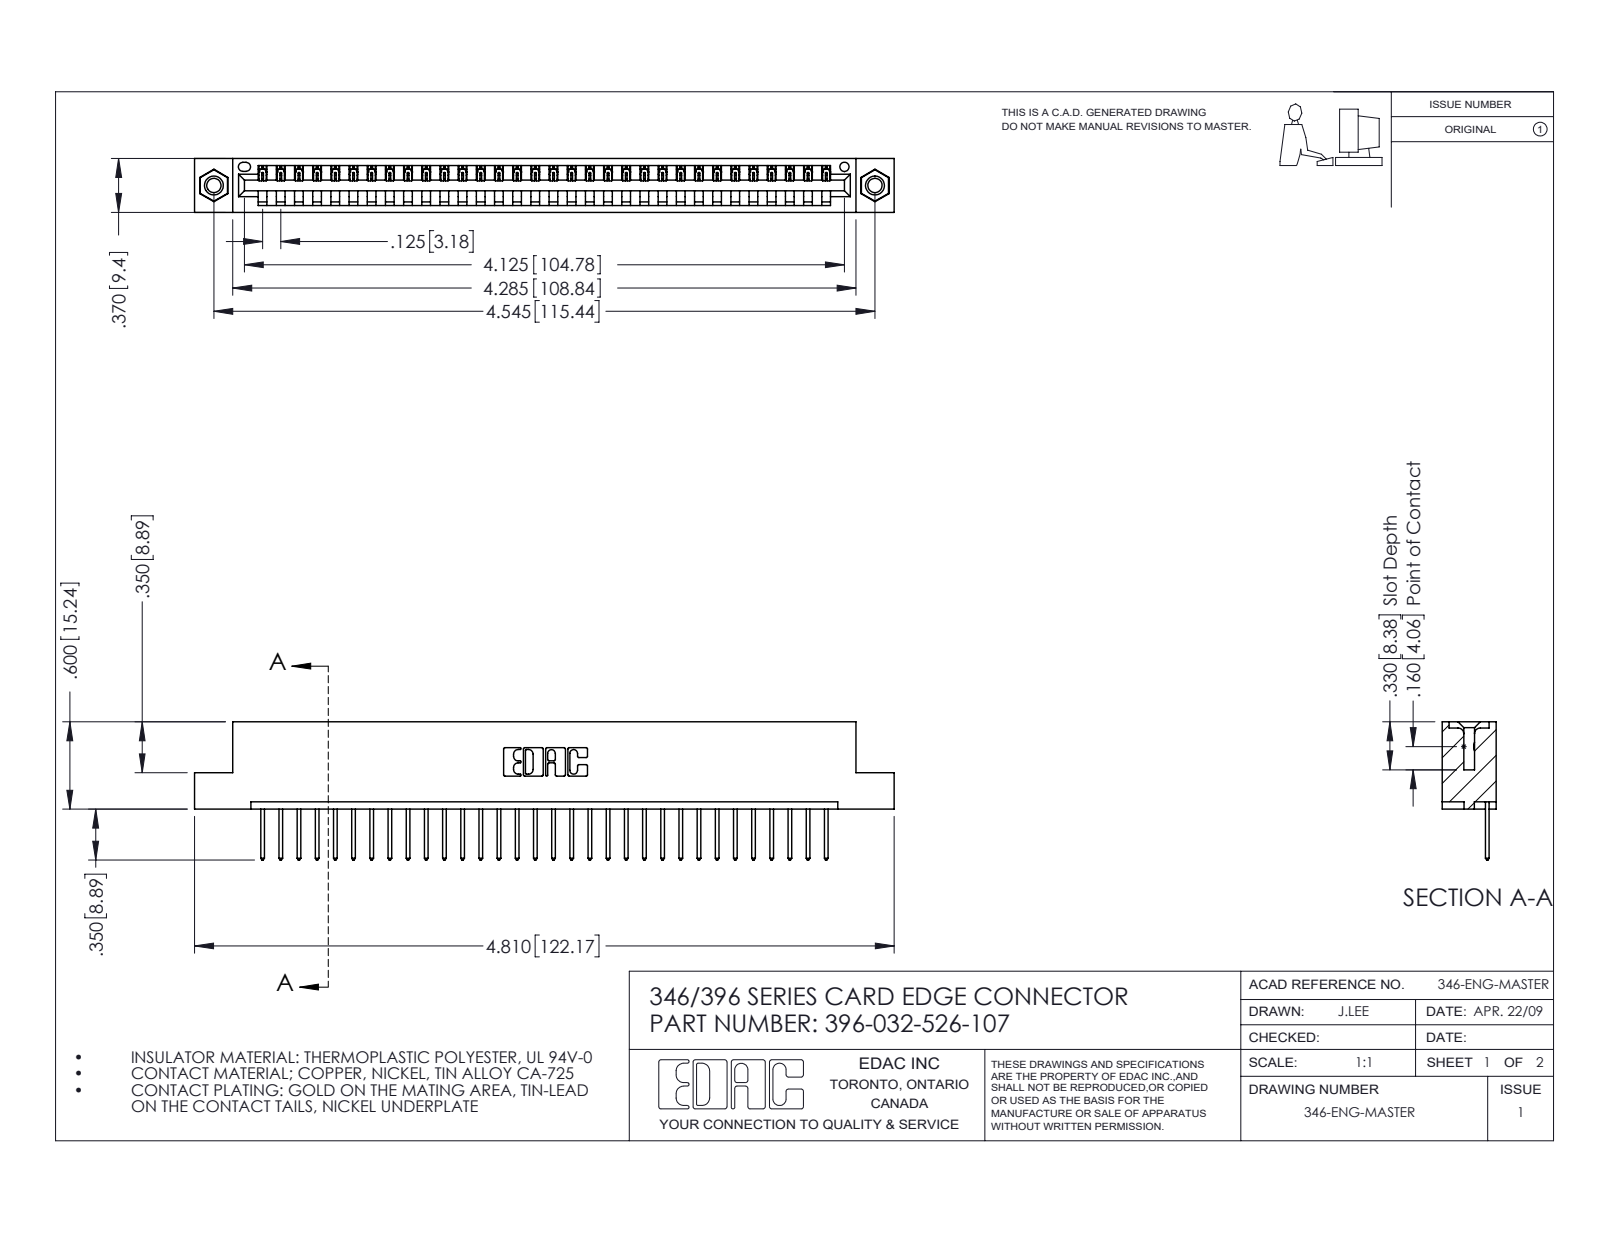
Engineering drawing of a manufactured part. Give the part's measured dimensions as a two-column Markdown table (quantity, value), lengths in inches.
| quantity | value |
| --- | --- |
| part name | 345-250-001_345-250-005-103; 345-292-001_345-293-126; 396-032-526-107; 346 Part_Flush Mounting Lugs - 0.156 Dia-TI |
| STEP written by | SolidWorks 2016 (CONFIG_CONTROL_DESIGN) |
| units | inches |
| bodies | 35 solids, 2038 faces (1388 planar, 634 cylindrical, 16 other) |
| overall size | 4.81 × 0.95 × 0.37 |
| volume | 0.707 in³ |
| surface area | 22.29 in² |
| round holes (diameter × count) | 0.098 × 2, 0.125 × 2, 0.156 × 2, 0.064 × 1 |
| round bosses / shafts (diameter × count) | 0.155 × 2 |
| partial cylindrical surfaces (radius × count) | 0.006 × 64, 0.01 × 64, 0.01 × 22, 0.007 × 6, 0.031 × 6, 0.026 × 3, 0.031 × 2, 0.04 × 2 |
| main face-to-face distances | 0.048, 0.322, 0.37, 0.25, 0.072, 0.298, 0.025, 0.148, 0.222, 0.1 |
| hole center spacings | 0.246, 4.337, 4.545 |
